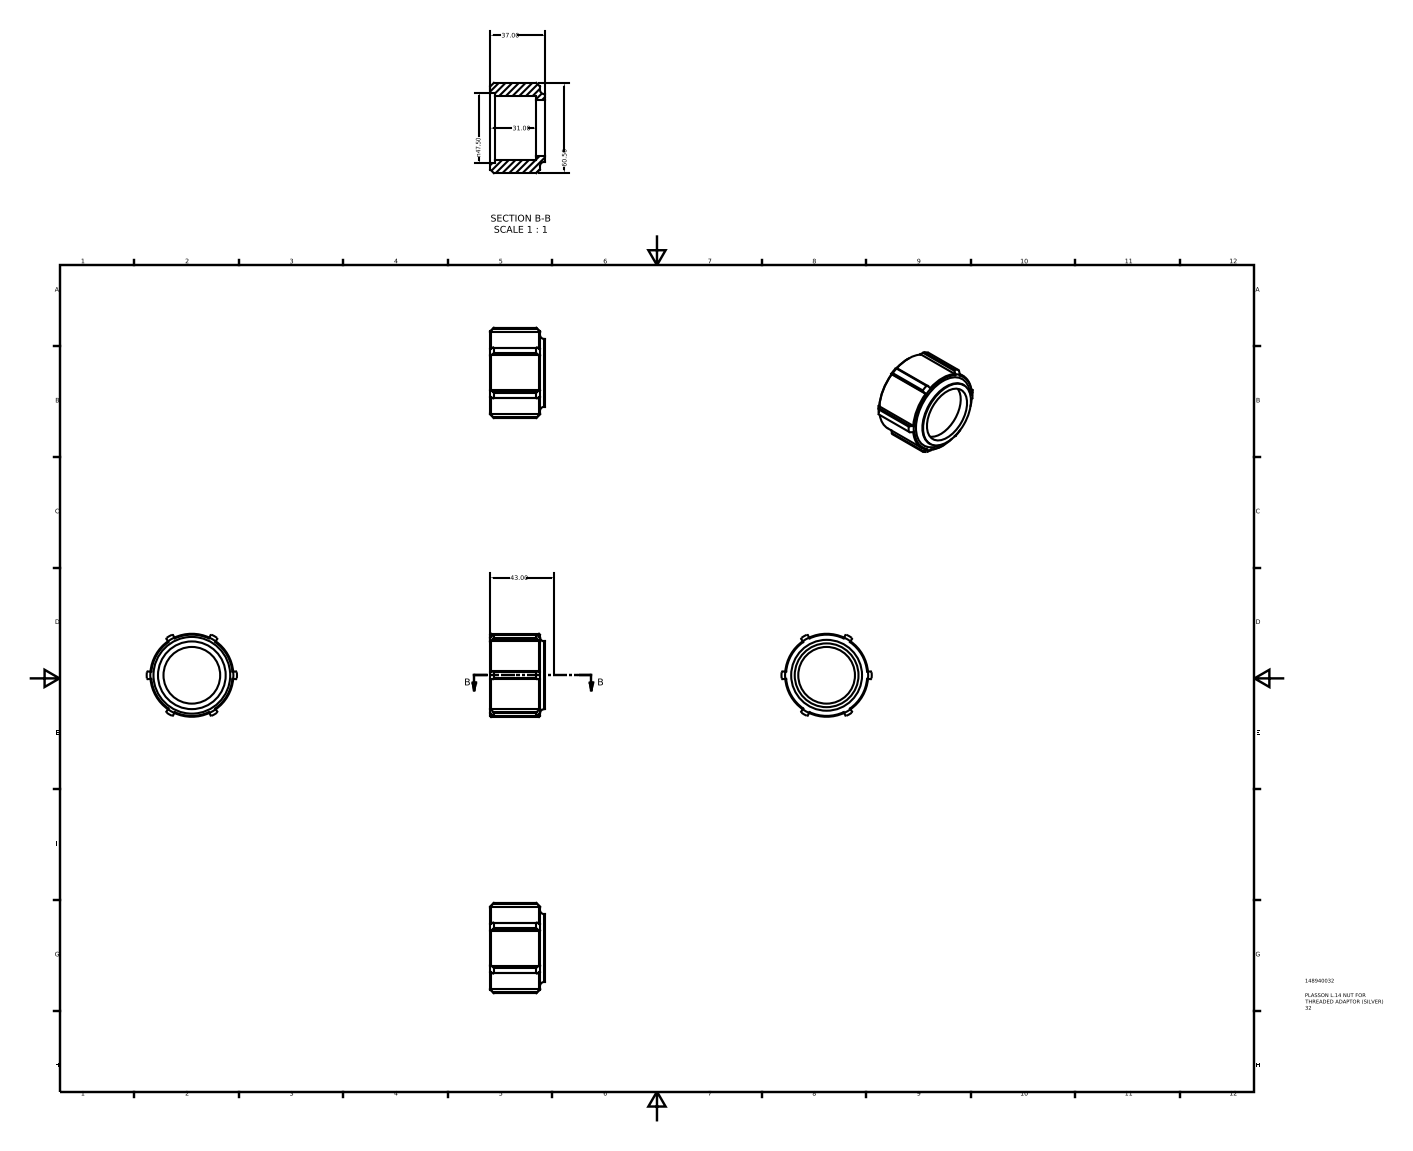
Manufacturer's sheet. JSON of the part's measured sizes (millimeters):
{"part_name": "148940032", "step_written_by": "Autodesk Inventor 2015 (AUTOMOTIVE_DESIGN)", "units": "millimeters", "bodies": {"solids": 1, "faces": 70, "planar": 29, "cylindrical": 16, "other": 25}, "overall_size": [60.5, 55.66, 37], "volume_mm3": 37106, "surface_area_mm2": 14503, "round_holes": [[38, 1], [42.75, 1], [47.5, 1]], "round_bosses_or_shafts": [[55.66, 1], [45.38, 1]], "partial_cylinders_radius": [[30.25, 1]], "face_to_face_distances": [37, 3.1, 33.9, 31, 27.9, 6, 33.3, 30.2, 2.3, 3.7]}
